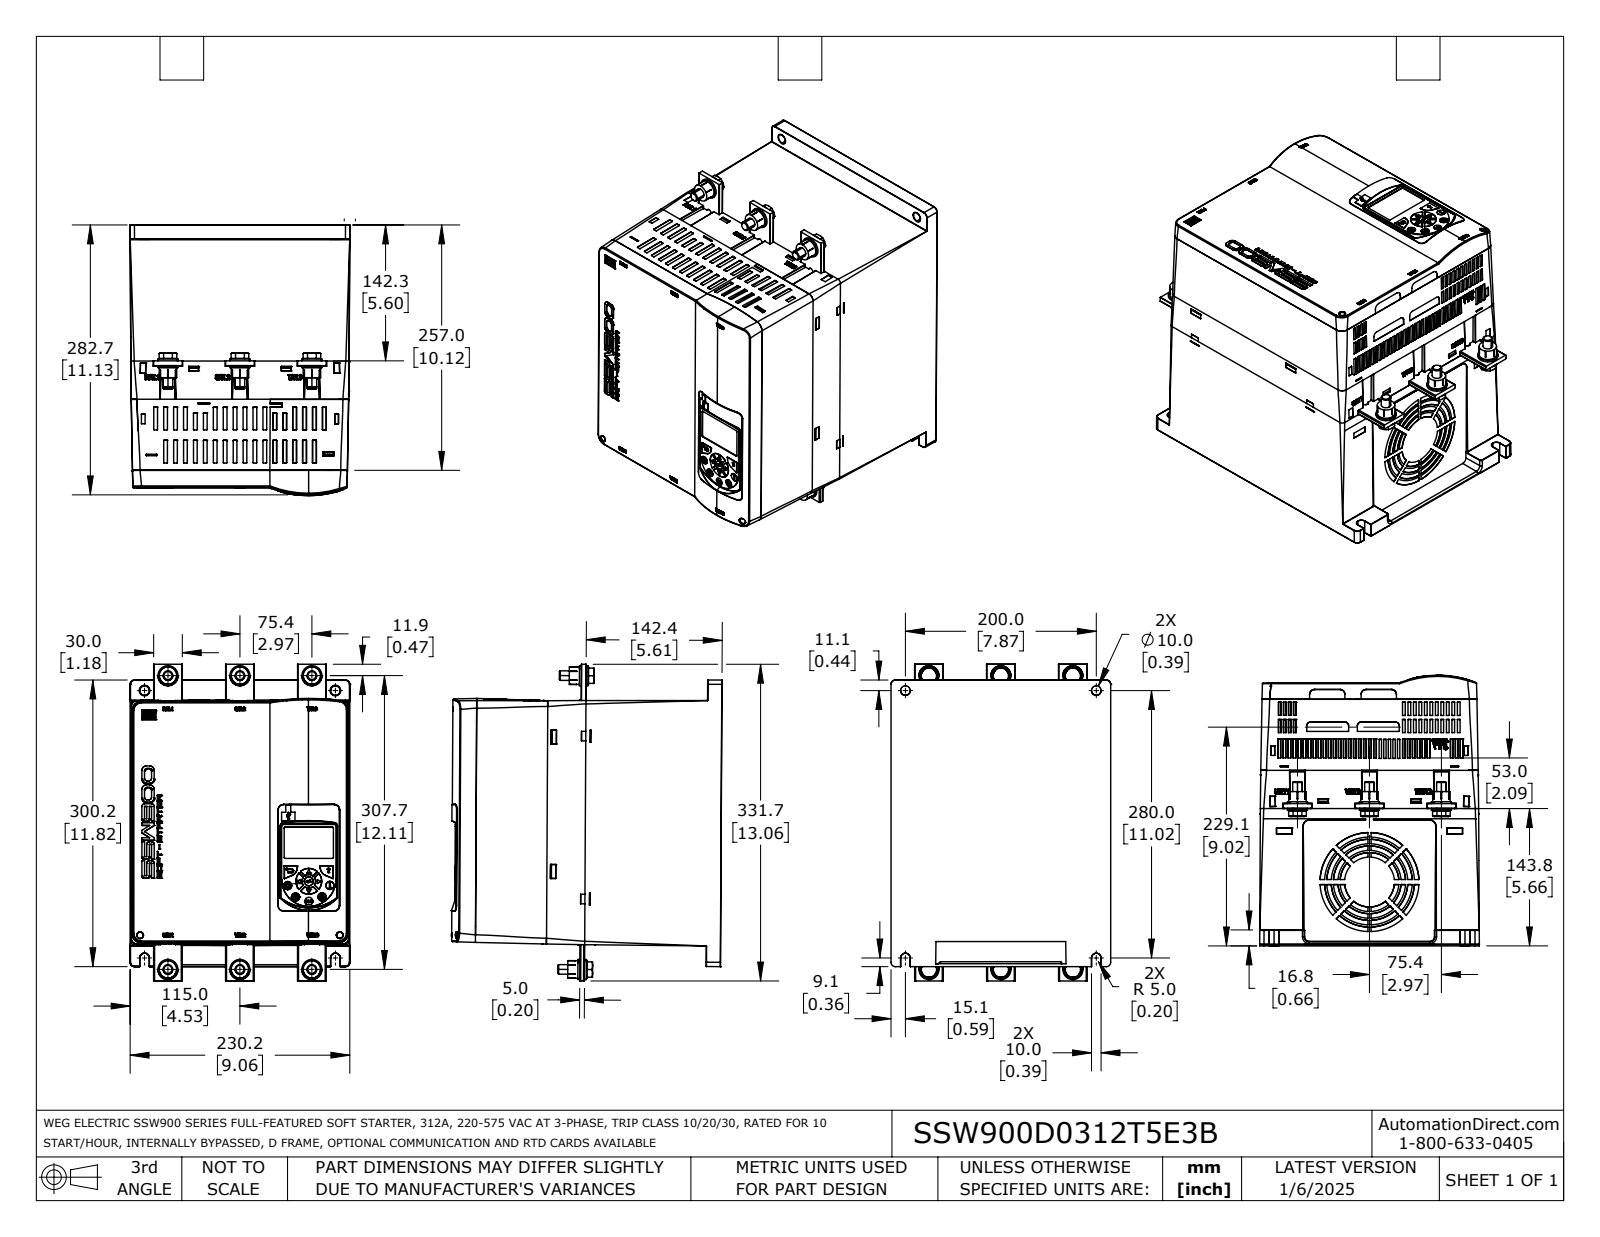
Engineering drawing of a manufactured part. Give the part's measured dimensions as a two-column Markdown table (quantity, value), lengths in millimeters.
| quantity | value |
| --- | --- |
| part name | SSW900D0312T5E3B |
| STEP written by | SolidWorks 2021 (AUTOMOTIVE_DESIGN) |
| units | millimeters |
| bodies | 1 solid, 4211 faces (2804 planar, 500 cylindrical, 907 other) |
| overall size | 331.7 × 283.5 × 230.1 |
| volume | 2 838 000 mm³ |
| surface area | 813 500 mm² |
| round holes (diameter × count) | 10 × 2, 3.4 × 1, 6.6 × 1, 61.7 × 1, 75.7 × 1, 89.7 × 1, 103.7 × 1 |
| round bosses / shafts (diameter × count) | 21 × 9, 18.3 × 6, 10 × 6, 94.3 × 1, 80.3 × 1, 66.3 × 1, 3.8 × 1, 1.4 × 1 |
| partial cylindrical surfaces (radius × count) | 0.3 × 103, 0.5 × 24, 0.4 × 22, 0.5 × 22, 0.5 × 20, 1 × 17, 0.2 × 7, 2 × 6 |
| main face-to-face distances | 17.9, 248.4, 274.2, 256.3, 2.5, 17.2, 257, 239.1, 14.8, 271.7 |
| hole center spacings | 200, 257.6, 328.9 |
